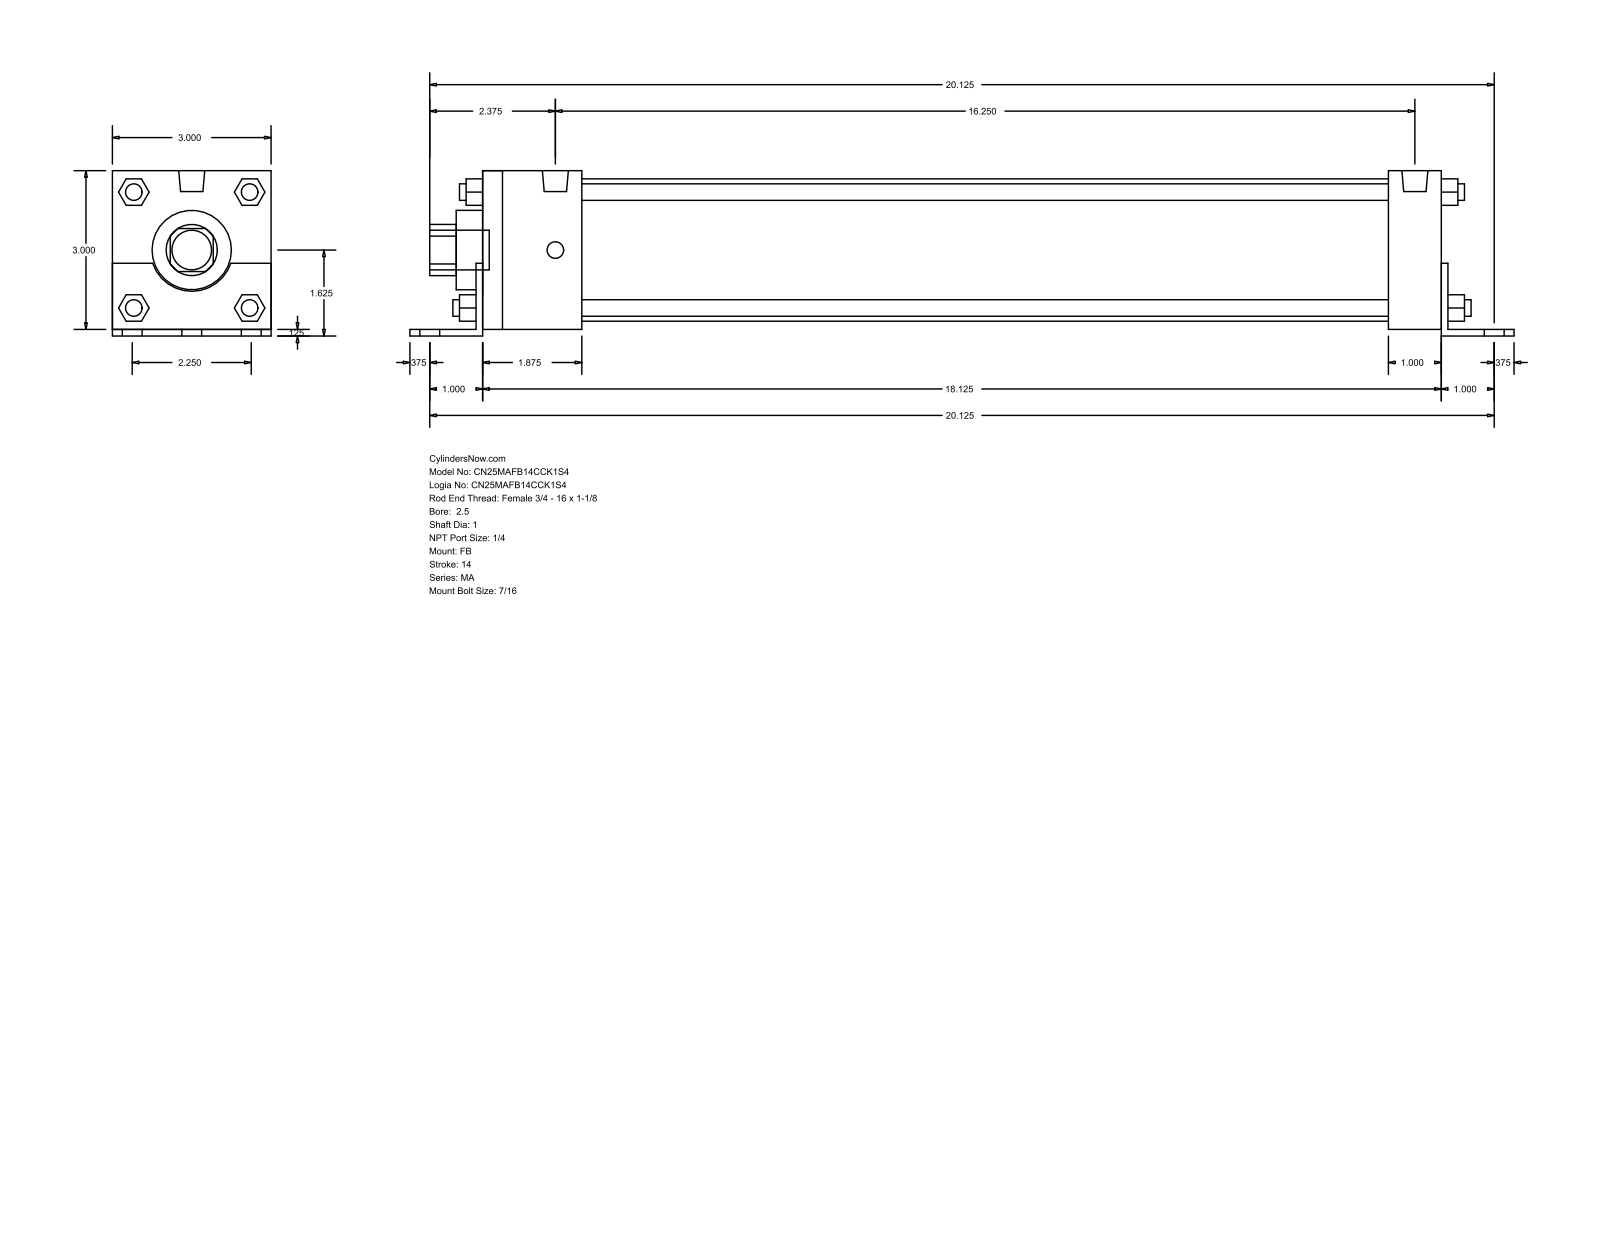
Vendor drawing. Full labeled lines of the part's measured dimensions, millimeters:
Part name (STEP PRODUCT): MA_FB__0250_1
STEP written by: GSSL Pune (CONFIG_CONTROL_DESIGN)
Units: millimetres
Bodies: 0 solids, 140 faces (105 planar, 35 cylindrical, 0 other)
Overall size (bounding box): 530.23 × 79.38 × 76.2
Round holes (diameter × count): ⌀25.4 ×1, ⌀38.1 ×1, ⌀68.33 ×1
Round bosses / shafts (diameter × count): ⌀7.94 ×8, ⌀11.11 ×6, ⌀12.49 ×2, ⌀19.05 ×1
Partial cylindrical surfaces — rounded edges, fillets, slot ends (radius × count): R12.29 ×1, R19.81 ×1
Main face-to-face distances: 76.2, 3.17, 79.37, 460.37, 3.18, 12.7, 463.55, 28.57, 47.63, 412.74
